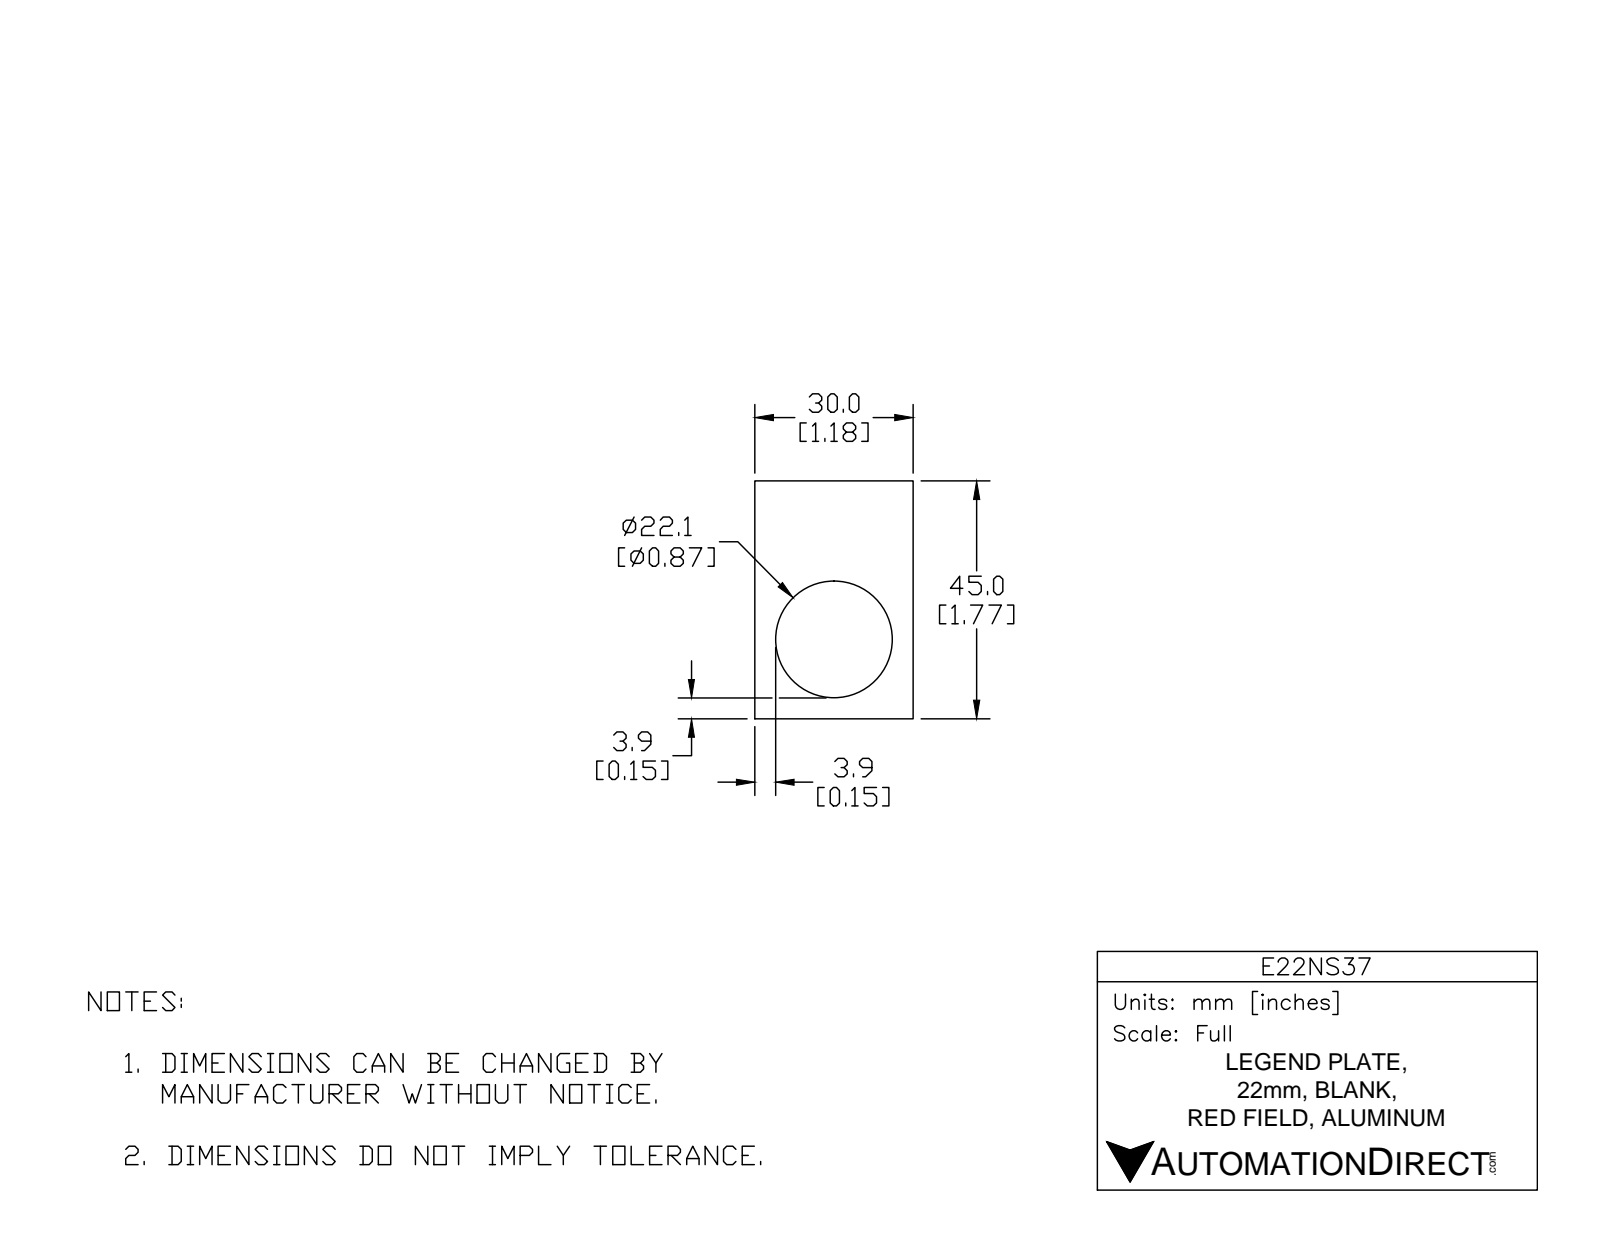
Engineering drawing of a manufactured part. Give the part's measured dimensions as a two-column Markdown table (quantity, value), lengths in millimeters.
| quantity | value |
| --- | --- |
| part name | E22NS37 |
| STEP written by | SolidWorks 2017 (AUTOMOTIVE_DESIGN) |
| units | millimeters |
| bodies | 1 solid, 12 faces (9 planar, 3 cylindrical, 0 other) |
| overall size | 45 × 30 × 1.3 |
| volume | 1 255 mm³ |
| surface area | 2 218 mm² |
| round holes (diameter × count) | 22.2 × 1 |
| main face-to-face distances | 1.3, 30, 45, 4.7, 40.3, 13.4, 16.6, 3.2 |
